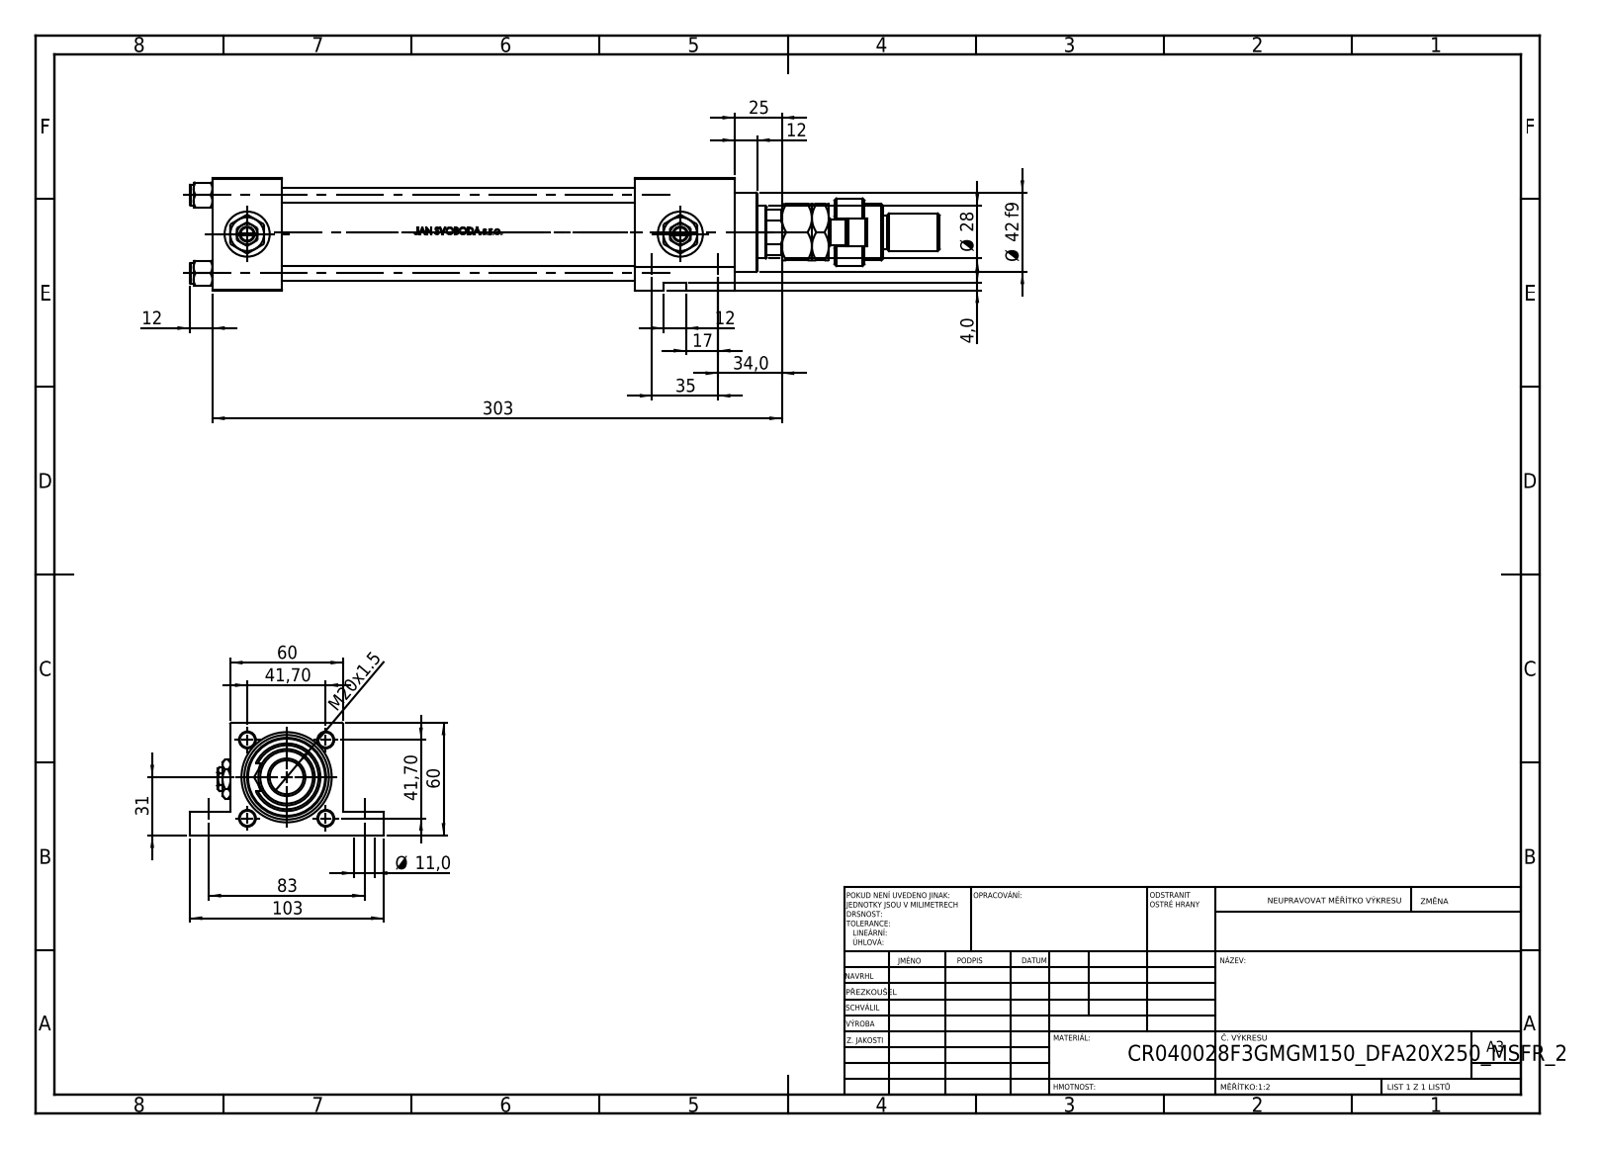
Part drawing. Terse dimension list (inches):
name: V215CR_F_Body; V215CR_VCP_F; V215_VC_A; Zatka_pro_OIL_PORT (+4 more)
written by: SolidWorks 2019 (CONFIG_CONTROL_DESIGN)
unit: in
bodies: 15 solids, 1300 faces (512 planar, 162 cylindrical, 626 other)
size: 15.709 × 4.055 × 2.362
volume: 39.64 in³; area: 299.9 in²
holes: 4× ⌀0.315, 4× ⌀0.433, 3× ⌀0.656, 3× ⌀0.945, 2× ⌀0.276, 1× ⌀0.63, 1× ⌀0.728, 1× ⌀1.102, 1× ⌀1.22, 1× ⌀1.575, 1× ⌀1.772
bosses: 4× ⌀0.433, 1× ⌀1.811, 1× ⌀1.654, 1× ⌀1.417, 1× ⌀1.181, 1× ⌀0.866, 1× ⌀0.787, 1× ⌀0.709
rounds: 1× R0.295, 1× R0.472, 1× R0.531
face distances: 2.362, 1.457, 2.087, 8.858, 7.402, 10.945, 1.496, 9.488, 0.492, 1.87
hole spacings: 1.642, 1.133, 1.189, 1.378, 2.322, 3.268, 3.546, 0.315
